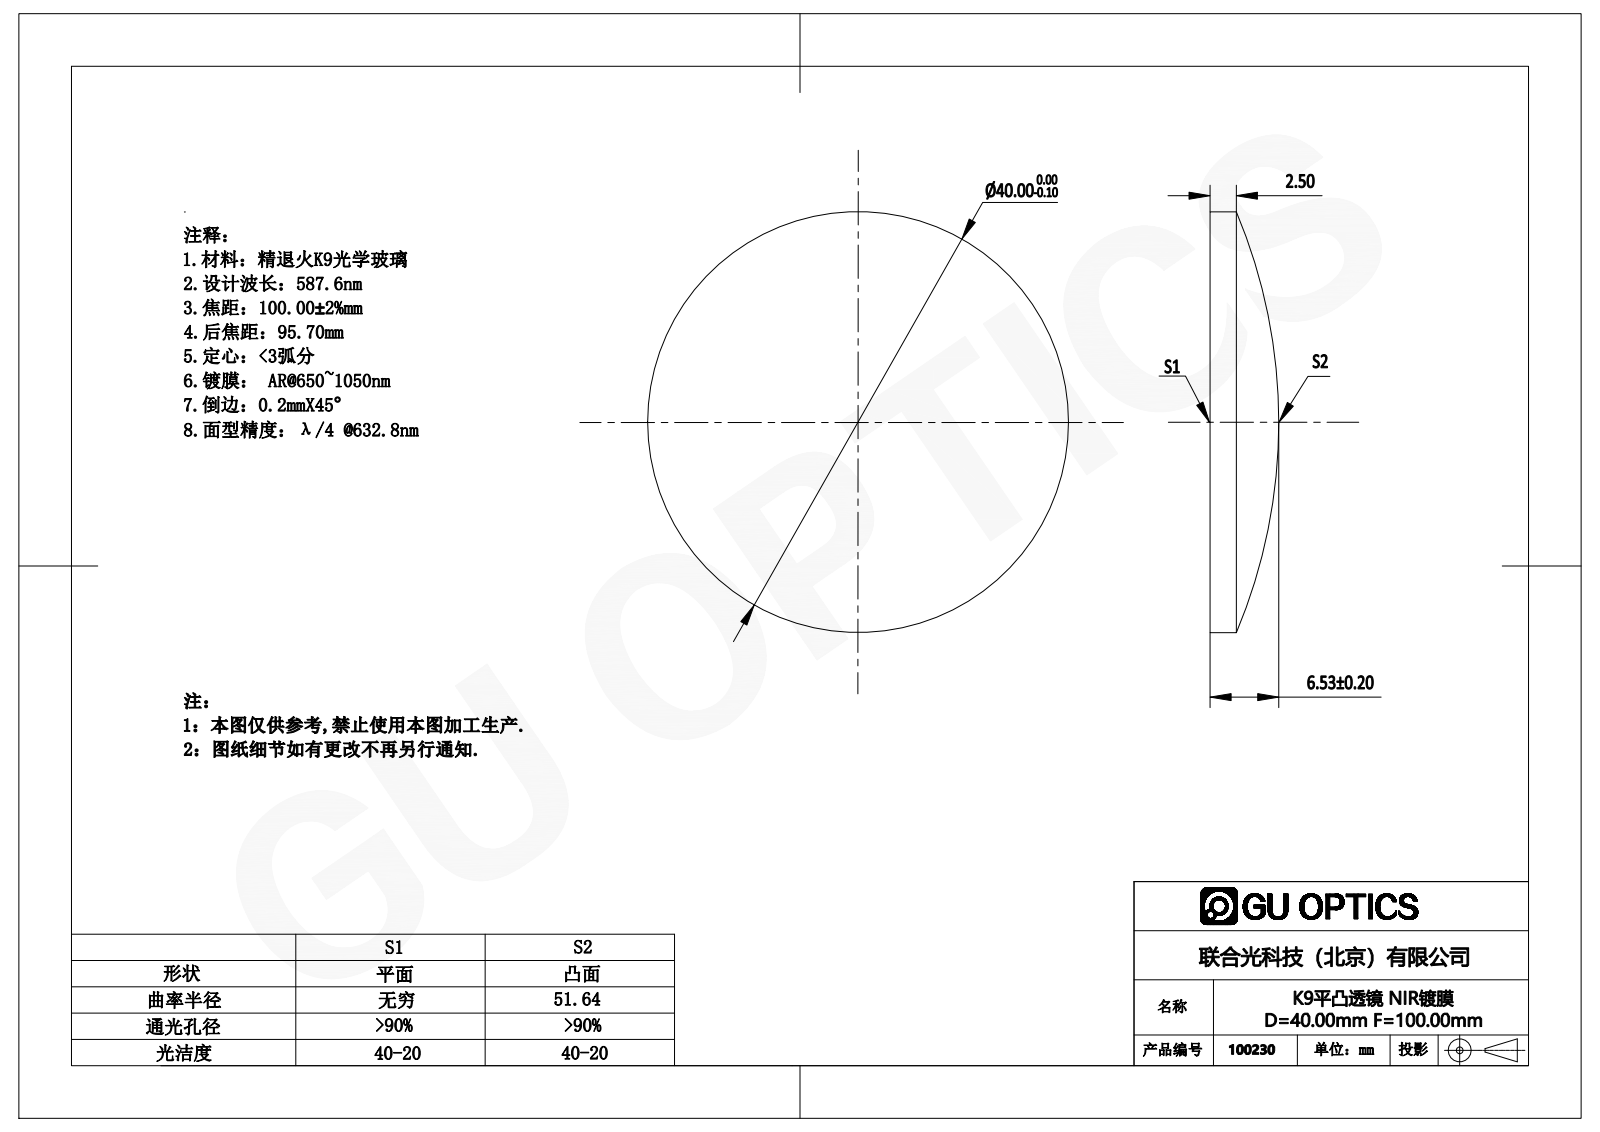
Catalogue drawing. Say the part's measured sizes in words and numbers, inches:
The part is named "100230". Its 3-D file was written by "SolidWorks 2016 (AUTOMOTIVE_DESIGN)". It is 1 solid with 5 faces: 1 planar, 2 cylindrical and 2 other. Overall it measures 1.575 by 1.575 by 0.257 inches. Its volume is 0.348 cubic inches and its surface area 4.461 square inches. Round bosses or shafts: 1 of diameter 1.575.
